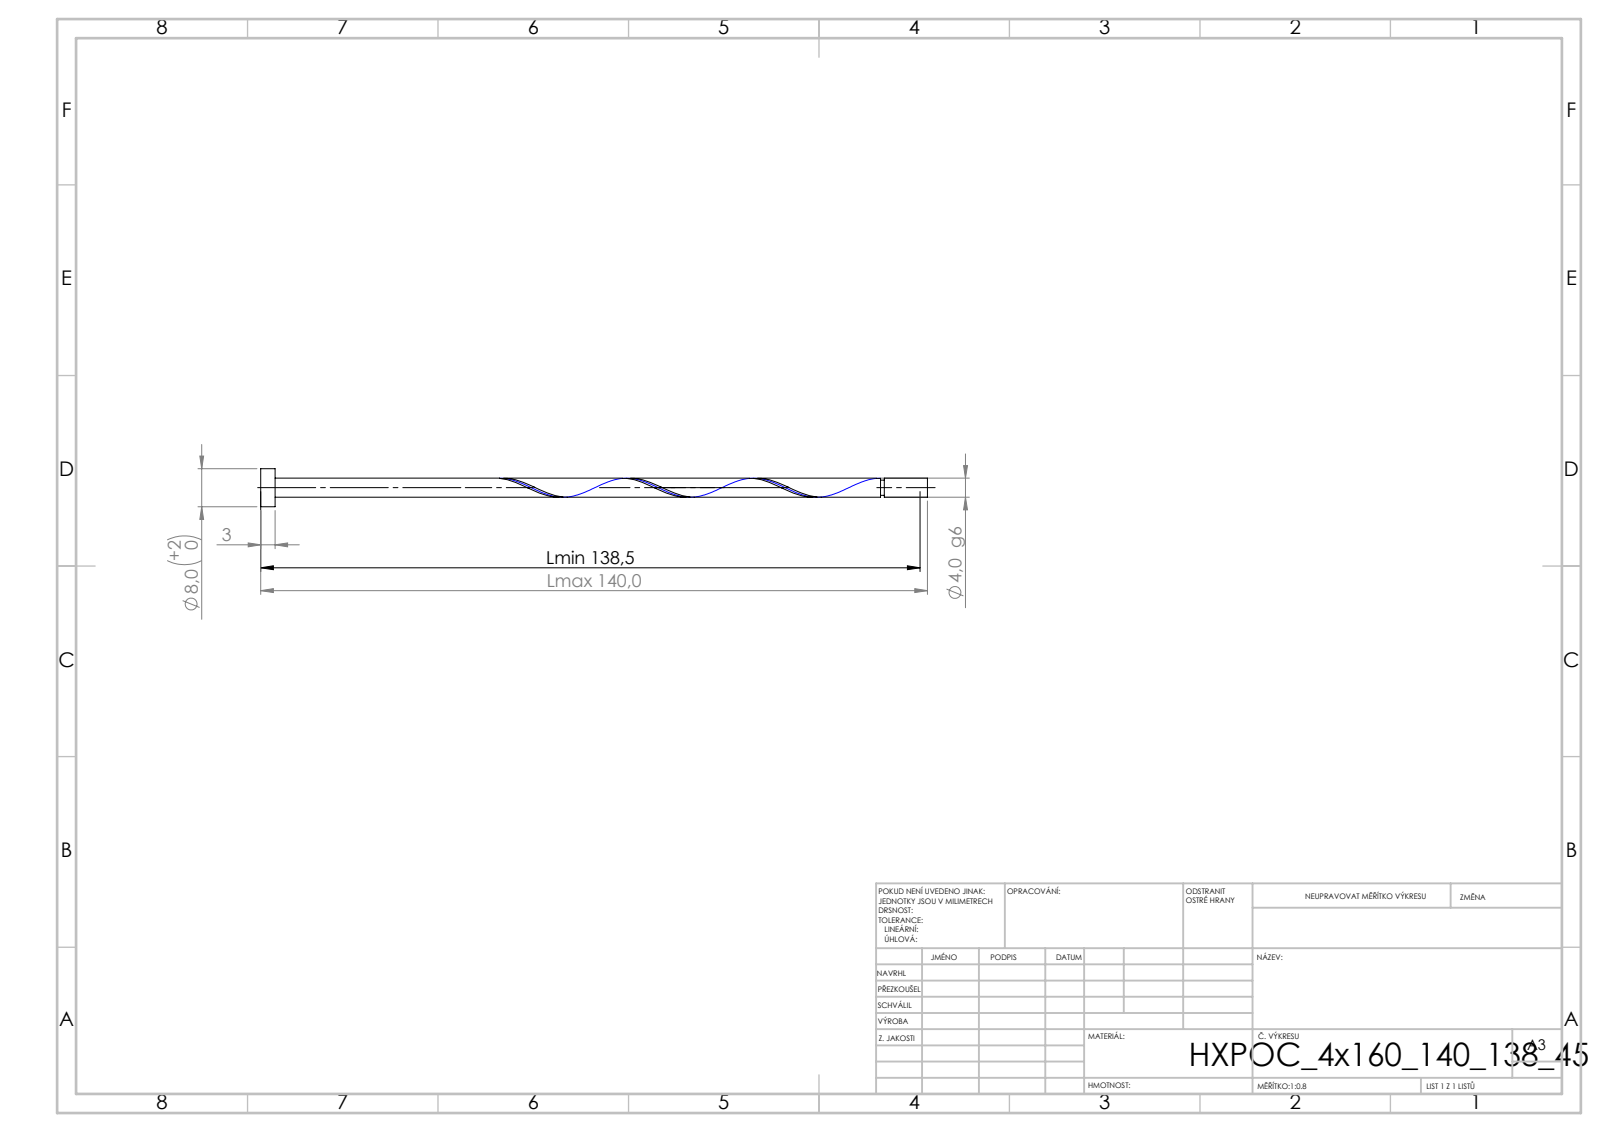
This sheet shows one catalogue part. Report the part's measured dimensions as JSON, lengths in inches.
{"step_written_by": "SolidWorks 2019 (CONFIG_CONTROL_DESIGN)", "units": "inches", "bodies": {"solids": 1, "faces": 21, "planar": 6, "cylindrical": 14, "other": 1}, "overall_size": [5.512, 0.315, 0.315], "volume_in3": 0.113, "surface_area_in2": 3.005, "round_bosses_or_shafts": [[0.315, 1], [0.157, 1], [0.126, 1]], "face_to_face_distances": [0.118, 5.512, 5.394, 5.156, 5.037, 0.356, 5.124, 5.006, 0.031, 0.388]}
